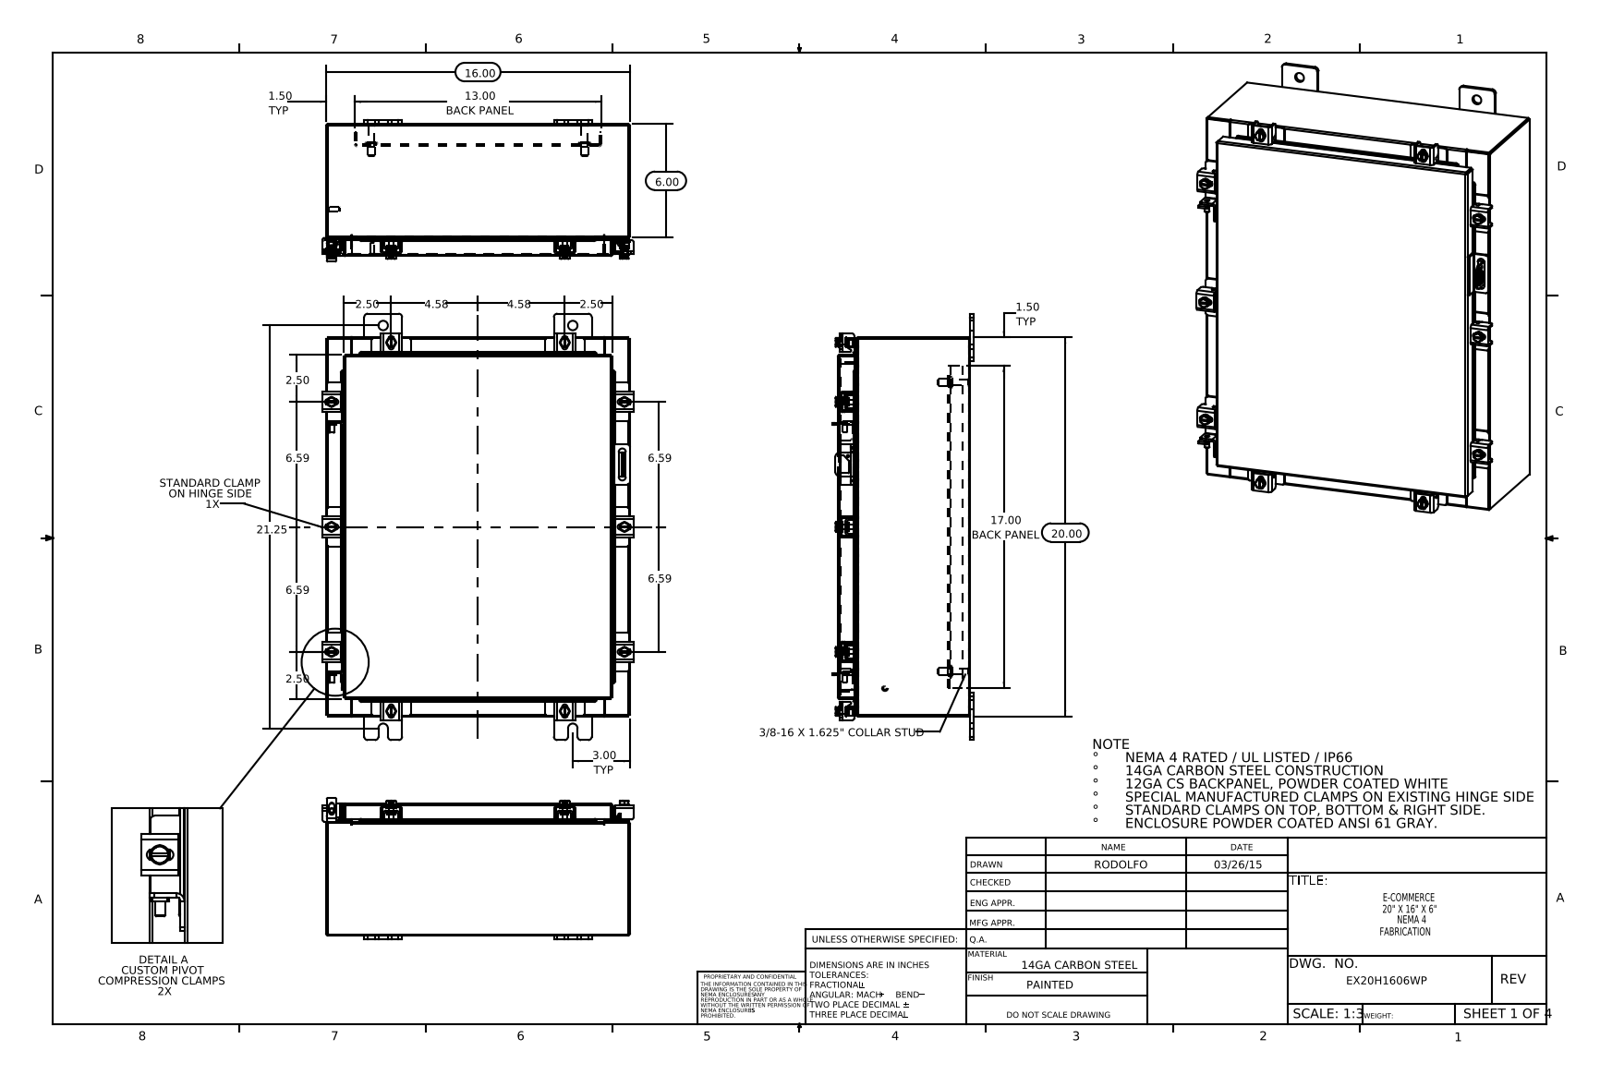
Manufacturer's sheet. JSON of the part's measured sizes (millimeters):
{"part_name": "ATEX CLAMP HINGE BRAKET; 22104005_DEFAULT_RTP30; EX20H1606WP Special Clamp; EX20H1606WP Body (+8 more)", "step_written_by": "SolidWorks 2014 (CONFIG_CONTROL_DESIGN)", "units": "millimeters", "bodies": {"solids": 71, "faces": 1784, "planar": 955, "cylindrical": 685, "other": 144}, "overall_size": [571.5, 417.1, 189.3], "volume_mm3": 2045000, "surface_area_mm2": 2012000, "round_holes": [[5.4, 10], [6.6, 10], [12.7, 8], [3.2, 1], [6.4, 1]], "round_bosses_or_shafts": [[12.7, 10], [6.4, 10], [10.1, 8], [15.9, 4], [9.5, 4], [8.4, 4], [8, 2], [6, 2]], "partial_cylinders_radius": [[1.5, 46], [0.3, 24], [4.8, 24], [2.2, 22], [3.6, 20], [3, 18], [2.3, 16], [2.5, 16]], "face_to_face_distances": [1.9, 175.3, 177.2, 173.4, 2.6, 404.5, 25.4, 27.3, 148, 149.9], "hole_center_spacings": [59.6, 112.8, 167.5, 259.6, 322.5, 365.1, 398.3, 422.1]}
